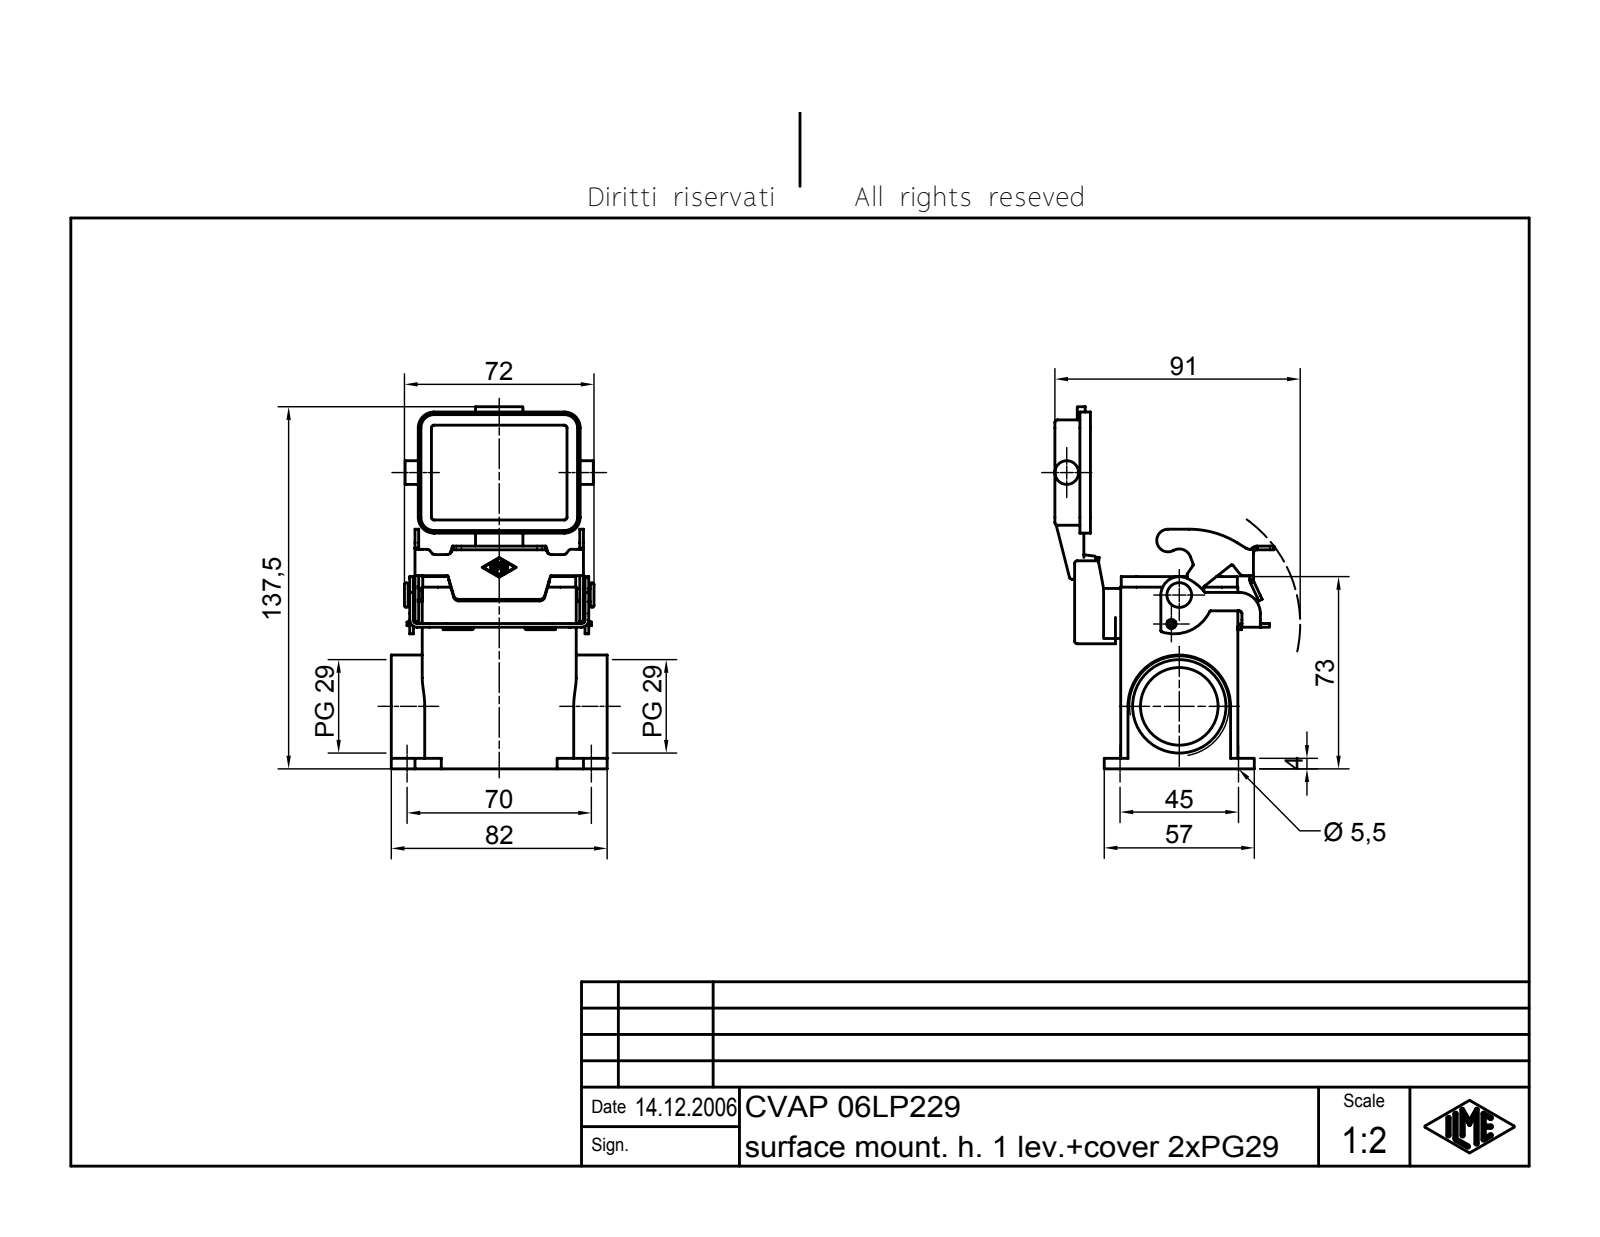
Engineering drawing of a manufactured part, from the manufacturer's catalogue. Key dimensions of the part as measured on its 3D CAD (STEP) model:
Part name (STEP PRODUCT): CVAP 06LP229
STEP written by: Autodesk Inventor 7 (AUTOMOTIVE_DESIGN)
Units: millimetres
Bodies: 4 solids, 592 faces (232 planar, 195 cylindrical, 165 other)
Overall size (bounding box): 137.5 × 83.23 × 82
Volume: 109 417 mm³ · Surface area: 63 327 mm²
Round holes (diameter × count): ⌀5.5 ×4, ⌀3.5 ×1, ⌀4 ×1, ⌀29.48 ×1, ⌀35.48 ×1
Round bosses / shafts (diameter × count): ⌀5 ×2, ⌀9 ×1, ⌀7 ×1, ⌀3.2 ×1, ⌀3 ×1
Partial cylindrical surfaces — rounded edges, fillets, slot ends (radius × count): R1 ×32, R0.25 ×15, R0.5 ×10, R1.5 ×9, R6 ×8, R2 ×7, R1.4 ×6, R2.8 ×6
Main face-to-face distances: 4, 40.5, 44.5, 2, 36.5, 69.5, 10.75, 13.5, 29, 65.5
Hole centre spacings: 45, 70, 83.22, 31.4
